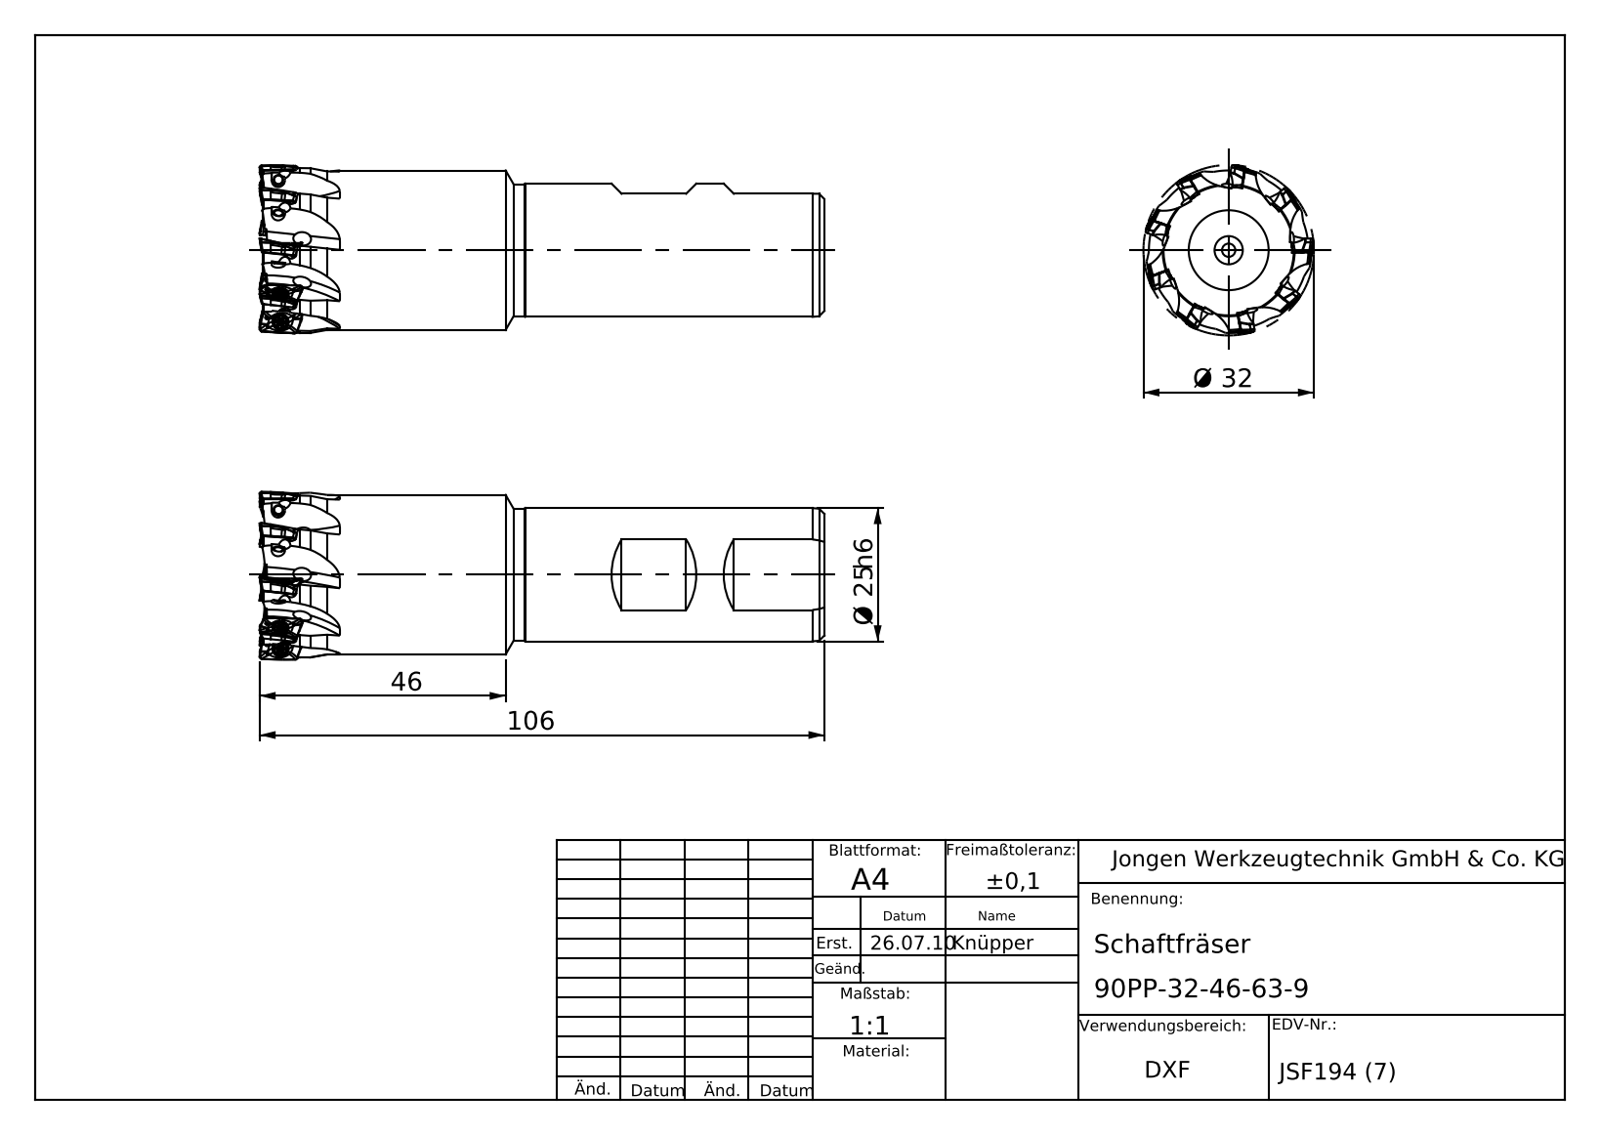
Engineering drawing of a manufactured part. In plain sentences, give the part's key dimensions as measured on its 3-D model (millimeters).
The part is named "90PP-32-46-63-9". Its 3-D file was written by "SolidWorks 2011 (AUTOMOTIVE_DESIGN)". It is 1 solid with 187 faces: 63 planar, 47 cylindrical and 77 other. Overall it measures 106 by 32 by 32 millimeters. Its volume is 56 891 cubic millimeters and its surface area 14 423 square millimeters. Round holes: 10 of diameter 2.5, 1 of diameter 6.5. Round bosses or shafts: 1 of diameter 29.94, 1 of diameter 25, 1 of diameter 24.8. Partial cylindrical surfaces (rounded edges, fillets, slot ends): 9 of radius 20, 1 of radius 15.53. The main face-to-face distances are 104.1, 105.5, 1.4, 14.88, 11.32, 26.2, 2, 2.01.
